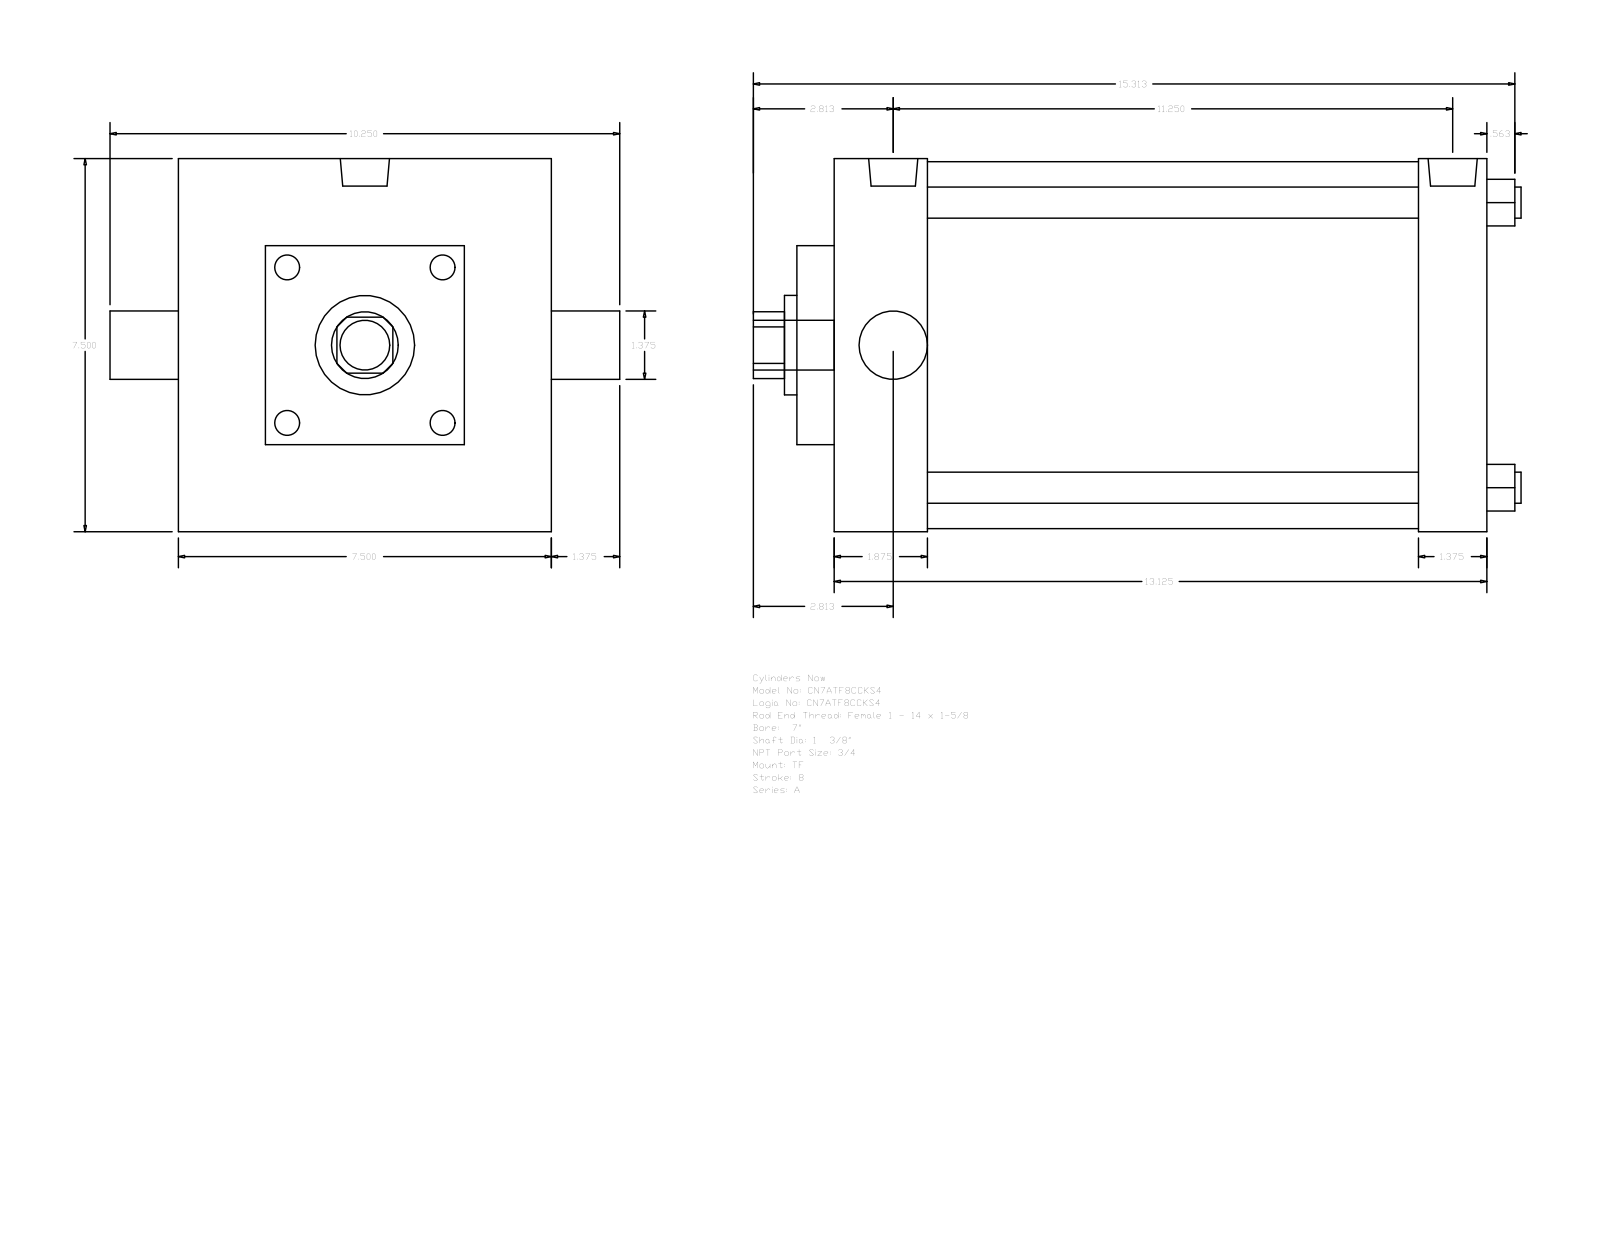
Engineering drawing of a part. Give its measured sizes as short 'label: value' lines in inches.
name: A_TF__0700_1.375
written by: GSSL Pune (CONFIG_CONTROL_DESIGN)
unit: in
bodies: 0 solids, 89 faces (65 planar, 24 cylindrical, 0 other)
size: 15.437 × 10.25 × 7.5
holes: 4× ⌀0.625, 2× ⌀1.375, 1× ⌀2, 1× ⌀7.375
bosses: 3× ⌀0.594, 2× ⌀0.989, 1× ⌀1
rounds: 1× R0.672
face distances: 7.5, 13.125, 0.75, 13.875, 2.625, 1.875, 11.25, 12.5, 11.75, 9.875
hole spacings: 4.052, 5.73, 8.103
